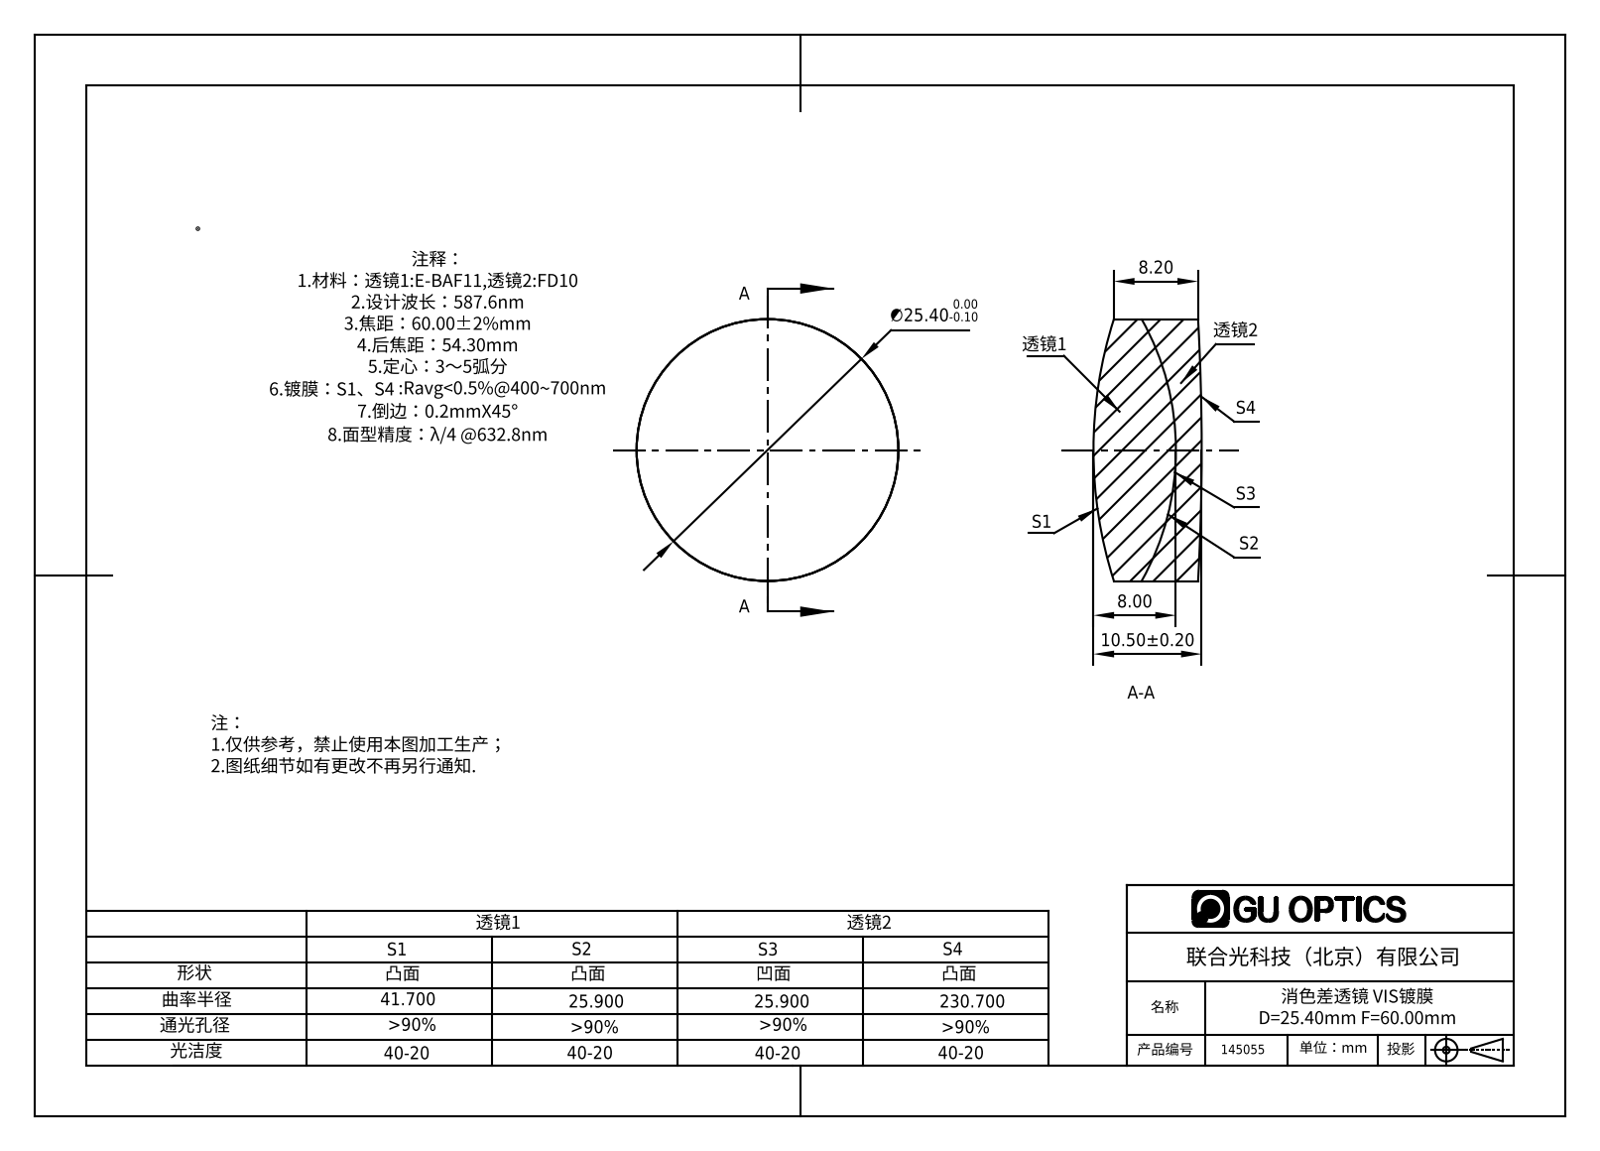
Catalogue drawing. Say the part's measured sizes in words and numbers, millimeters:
The part is named "145055". Its 3-D file was written by "SolidWorks 2016 (AUTOMOTIVE_DESIGN)". It is 2 solids with 12 faces: 0 planar, 4 cylindrical and 8 other. Overall it measures 25.4 by 25.4 by 10.5 millimeters. Its volume is 4 734 cubic millimeters and its surface area 2 761 square millimeters. Round bosses or shafts: 1 of diameter 25.4.
